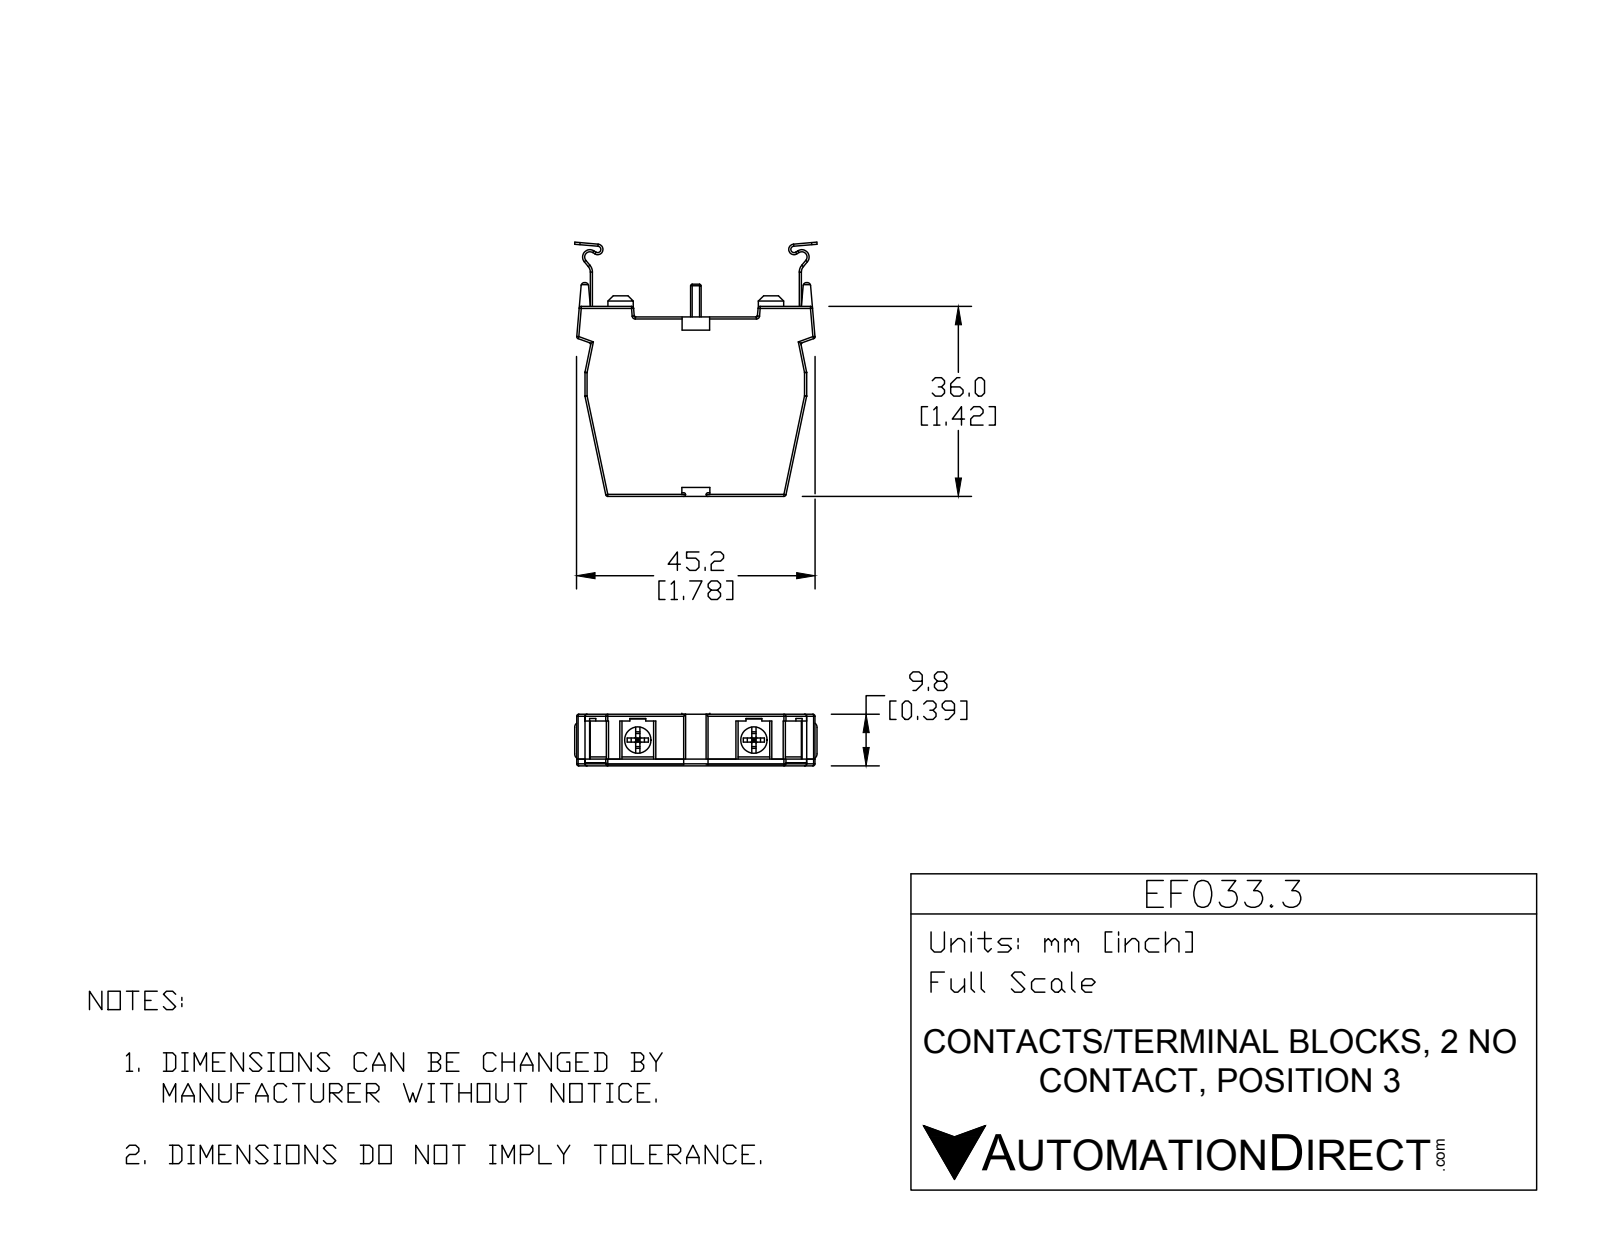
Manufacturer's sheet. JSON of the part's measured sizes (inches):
{"part_name": "EF033.3", "step_written_by": "SolidWorks 2015 (AUTOMOTIVE_DESIGN)", "units": "inches", "bodies": {"solids": 7, "faces": 299, "planar": 173, "cylindrical": 104, "other": 22}, "overall_size": [1.896, 1.822, 0.386], "volume_in3": 0.741, "surface_area_in2": 10.24, "round_holes": [[0.197, 4]], "round_bosses_or_shafts": [[0.157, 4], [0.187, 2]], "partial_cylinders_radius": [[0.01, 44], [0.02, 8], [0.039, 6], [0.024, 4], [0.024, 2], [0.039, 2], [0.055, 2], [0.063, 2]], "face_to_face_distances": [0.386, 0.055, 0.331, 1.339, 0.276, 0.079, 0.016, 0.125, 1.464, 1.417], "hole_center_spacings": [0.859]}
